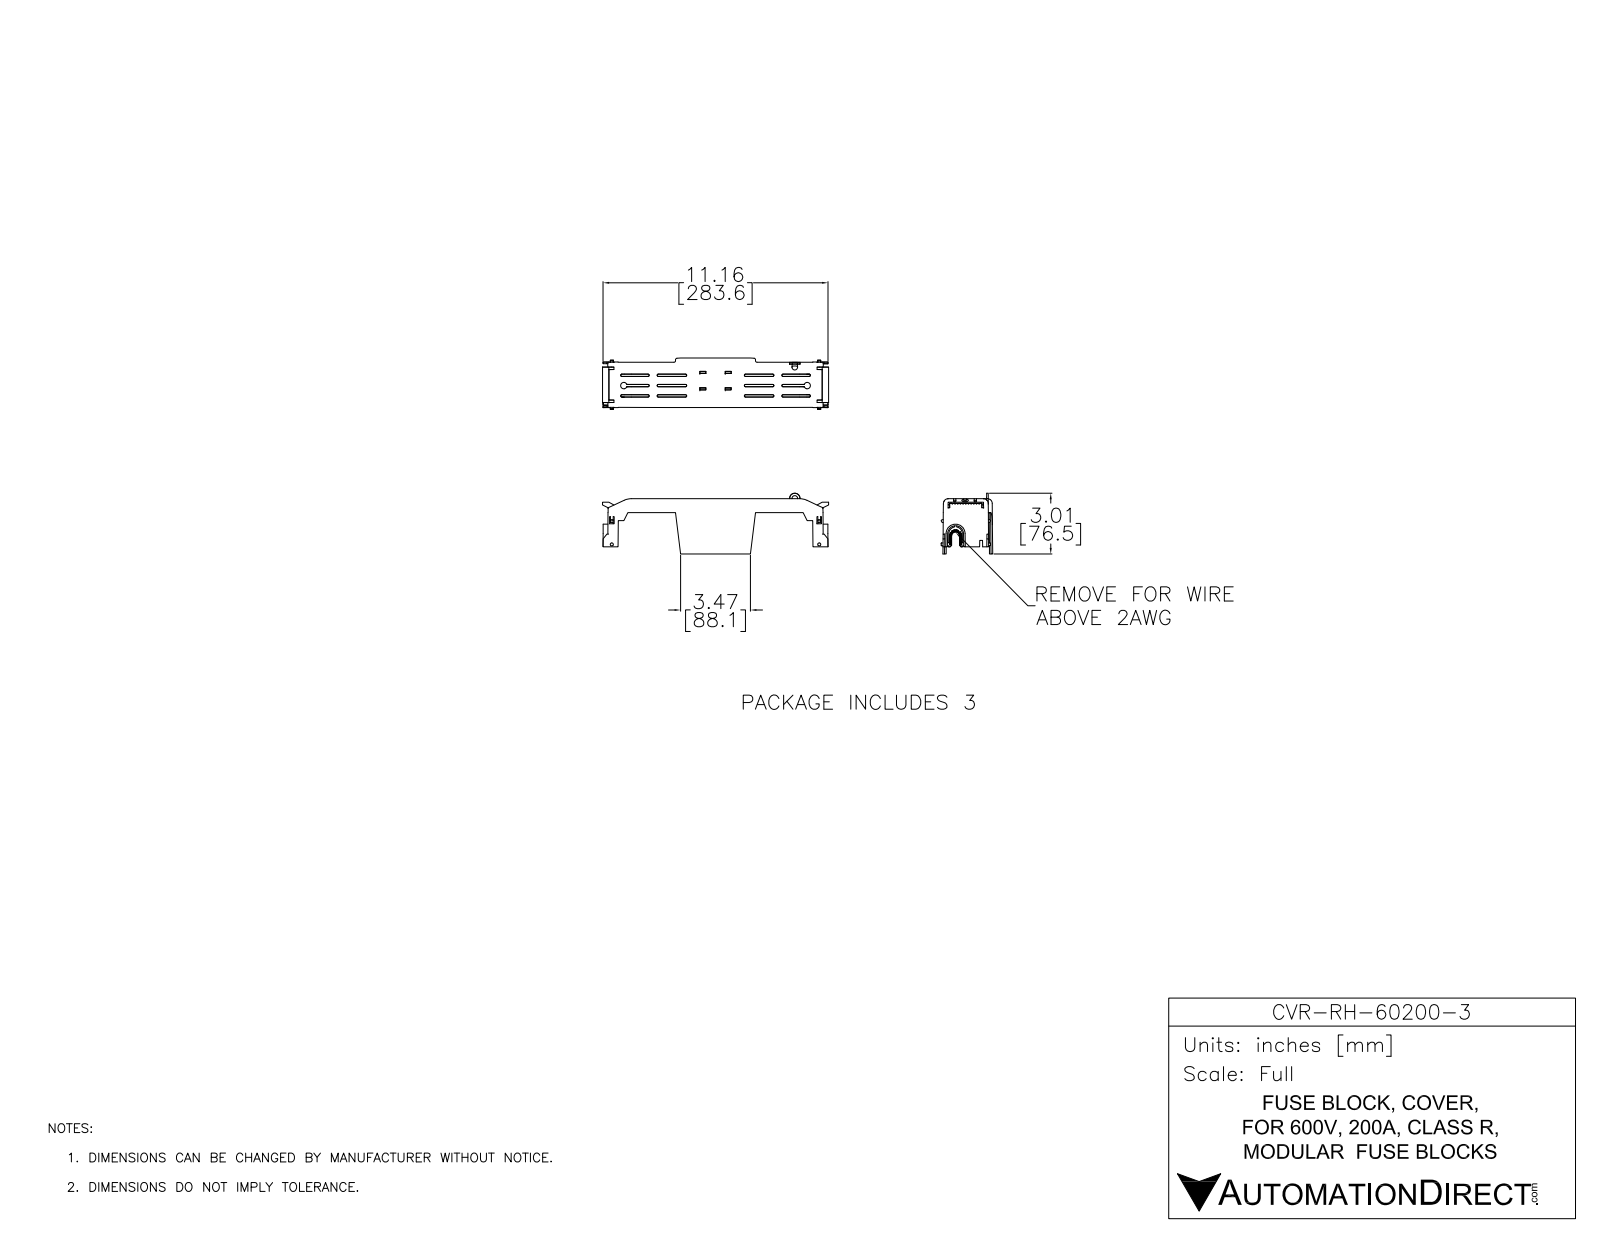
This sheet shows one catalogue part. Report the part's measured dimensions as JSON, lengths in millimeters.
{"part_name": "CVR-RH-60200-3", "step_written_by": "SolidWorks 2017 (AUTOMOTIVE_DESIGN)", "units": "millimeters", "bodies": {"solids": 1, "faces": 1446, "planar": 937, "cylindrical": 106, "other": 403}, "overall_size": [284.9, 76.5, 64.8], "volume_mm3": 90180, "surface_area_mm2": 96260, "round_holes": [[7, 1]], "partial_cylinders_radius": [[1, 16], [3, 8], [4, 7], [6, 7], [2, 6], [0.3, 2], [0.5, 2], [5, 2]], "face_to_face_distances": [2, 5, 3, 7, 13, 20.4, 15.8, 42.7, 44.7, 32.2]}
